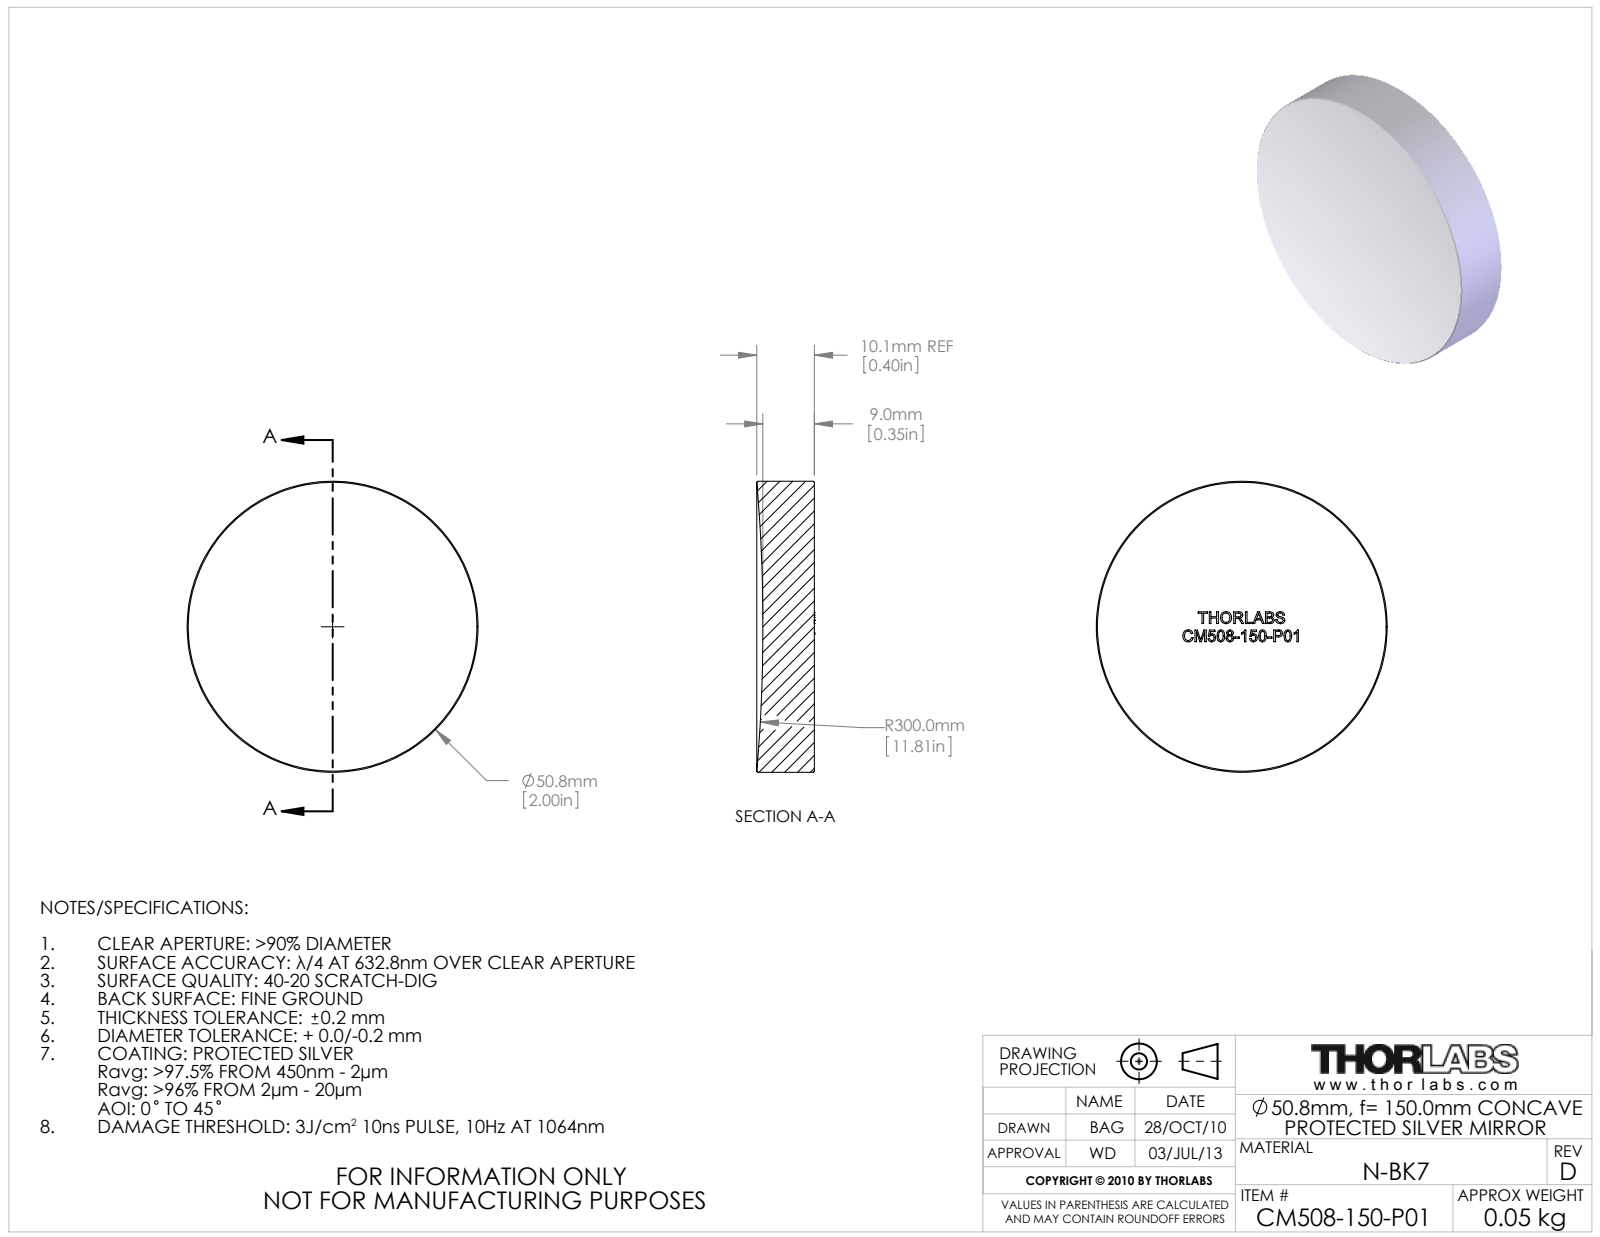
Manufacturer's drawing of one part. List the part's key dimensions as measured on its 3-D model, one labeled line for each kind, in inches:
Part name (STEP PRODUCT): 17573-E0W
STEP written by: SolidWorks 2012 (CONFIG_CONTROL_DESIGN)
Units: inches
Bodies: 1 solid, 281 faces (147 planar, 2 cylindrical, 132 other)
Overall size (bounding box): 2 × 2 × 0.396
Volume: 1.179 in³ · Surface area: 8.72 in²
Round bosses / shafts (diameter × count): ⌀2 ×1
Main face-to-face distances: 0.081, 0.062, 0.218, 0.083, 0.149, 0.038, 0.098, 0.091, 0.124, 0.1
